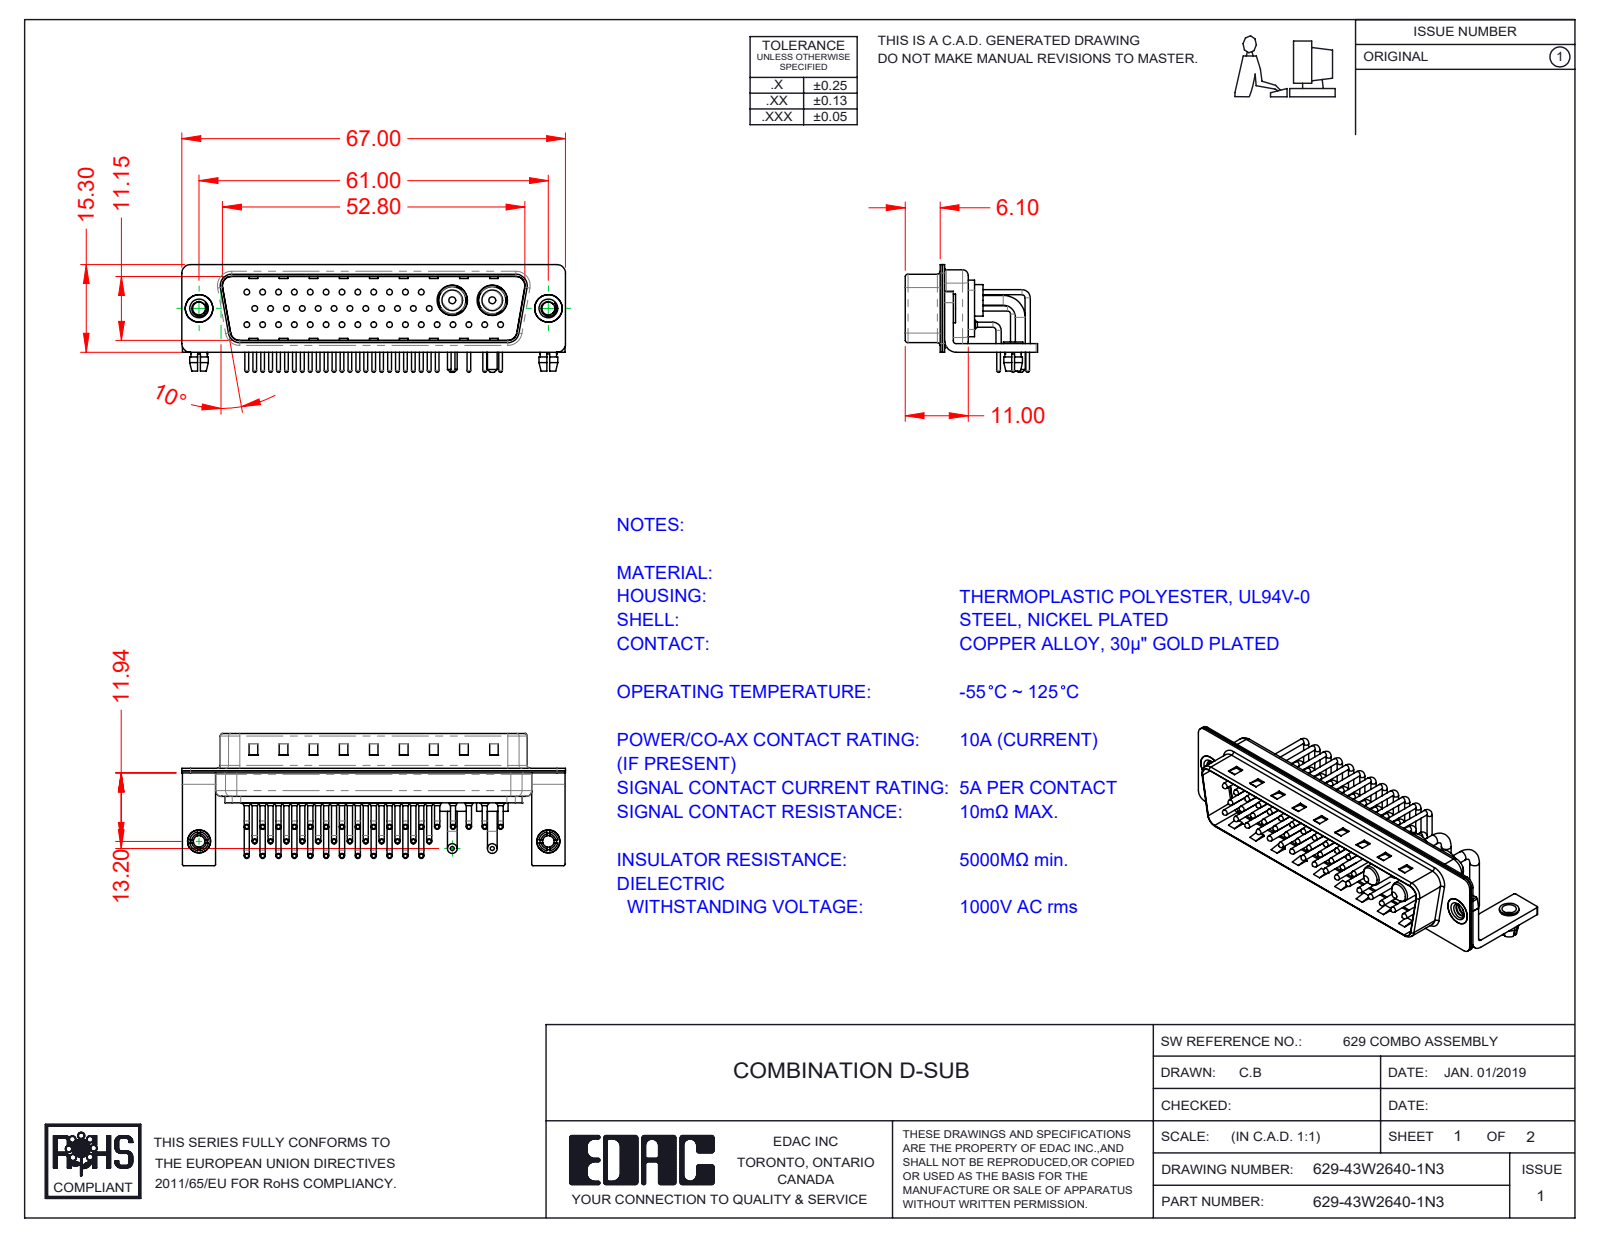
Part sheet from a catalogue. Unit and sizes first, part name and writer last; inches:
Units: inches
Overall size (bounding box): 2.638 × 0.909 × 0.74
Round holes (diameter × count): ⌀0.079 ×43, ⌀0.03 ×41, ⌀0.063 ×41, ⌀0.089 ×2, ⌀0.098 ×2, ⌀0.126 ×2, ⌀0.157 ×2, ⌀0.189 ×2, ⌀0.191 ×2, ⌀0.209 ×2
Round bosses / shafts (diameter × count): ⌀0.035 ×82, ⌀0.059 ×41, ⌀0.039 ×41, ⌀0.026 ×41, ⌀0.067 ×4, ⌀0.217 ×2, ⌀0.205 ×2, ⌀0.197 ×2
Partial cylindrical surfaces — rounded edges, fillets, slot ends (radius × count): R0.04 ×41, R0.01 ×16, R0.059 ×16, R0.079 ×13, R0.02 ×9, R0.063 ×8, R0.024 ×4, R0.026 ×4
Main face-to-face distances: 0.016, 0.059, 0.455, 0.22, 0.205, 0.031, 0.075, 0.161, 0.236, 0.031
Hole centre spacings: 0.109, 0.218, 0.124, 0.327, 0.436, 0.545, 0.654, 0.763
Volume: 0.332 in³ · Surface area: 20.74 in²
Bodies: 54 solids, 5140 faces (2915 planar, 1709 cylindrical, 516 other)
Part name (STEP PRODUCT): 629Combo Contact Row 2_50 Contacts; 629-43W2640-1N3; 629Combo Shell Rear_50 Contacts; Power Pin_10A RA 50 (+7 more)
STEP written by: SolidWorks 2020 (CONFIG_CONTROL_DESIGN)
